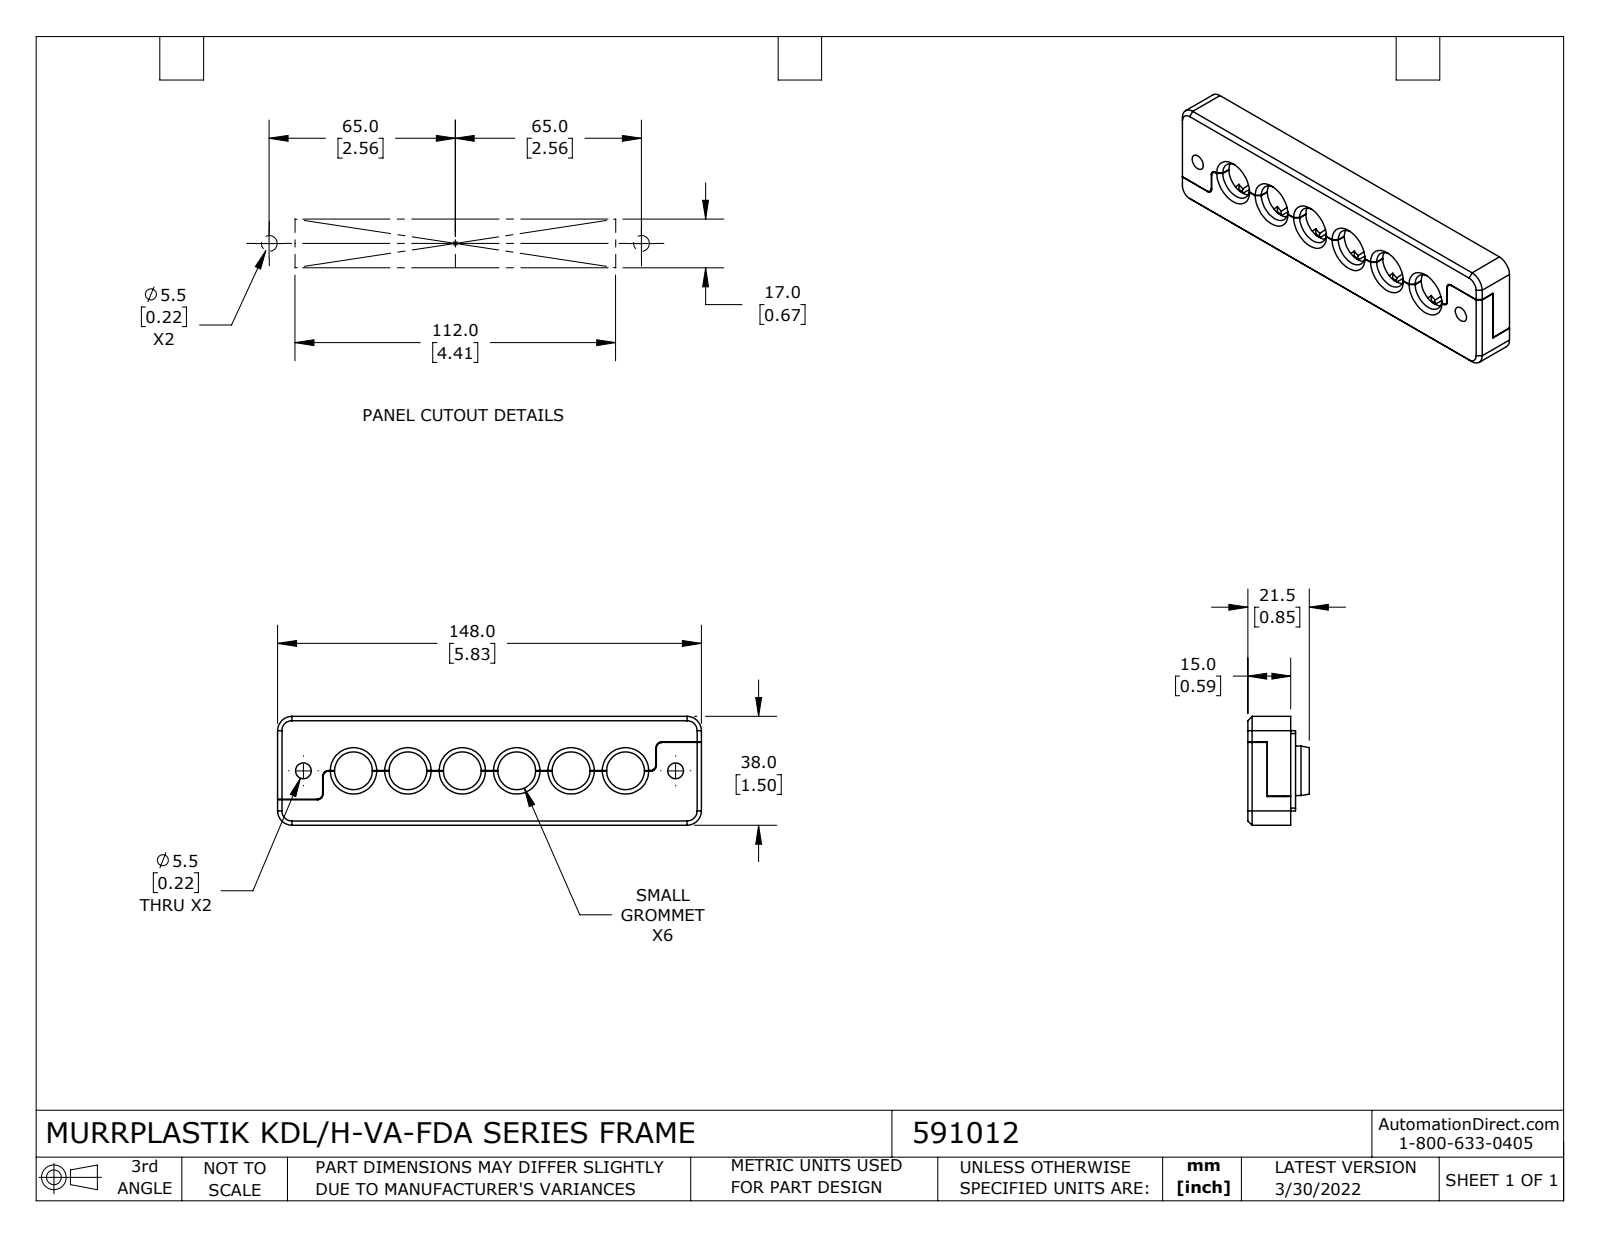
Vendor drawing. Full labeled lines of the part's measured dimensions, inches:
Part name (STEP PRODUCT): 591012
STEP written by: SolidWorks 2021 (CONFIG_CONTROL_DESIGN)
Units: inches
Bodies: 3 solids, 452 faces (256 planar, 131 cylindrical, 65 other)
Overall size (bounding box): 5.827 × 1.496 × 0.846
Volume: 4.187 in³ · Surface area: 56.62 in²
Round holes (diameter × count): ⌀0.52 ×6, ⌀0.589 ×5, ⌀0.217 ×2, ⌀0.236 ×2, ⌀0.335 ×2, ⌀0.591 ×1
Round bosses / shafts (diameter × count): ⌀0.291 ×2
Partial cylindrical surfaces — rounded edges, fillets, slot ends (radius × count): R0.039 ×9, R0.079 ×8, R0.098 ×8, R0.012 ×6, R0.004 ×4, R0.016 ×4, R0.02 ×4, R0.197 ×4
Main face-to-face distances: 0.177, 0.197, 1.319, 1.299, 1.496, 0.02, 1.122, 0.413, 0.472, 0.65
Hole centre spacings: 0.748, 1.496, 2.244, 0.315, 0.689, 0.757, 1.437, 1.471
